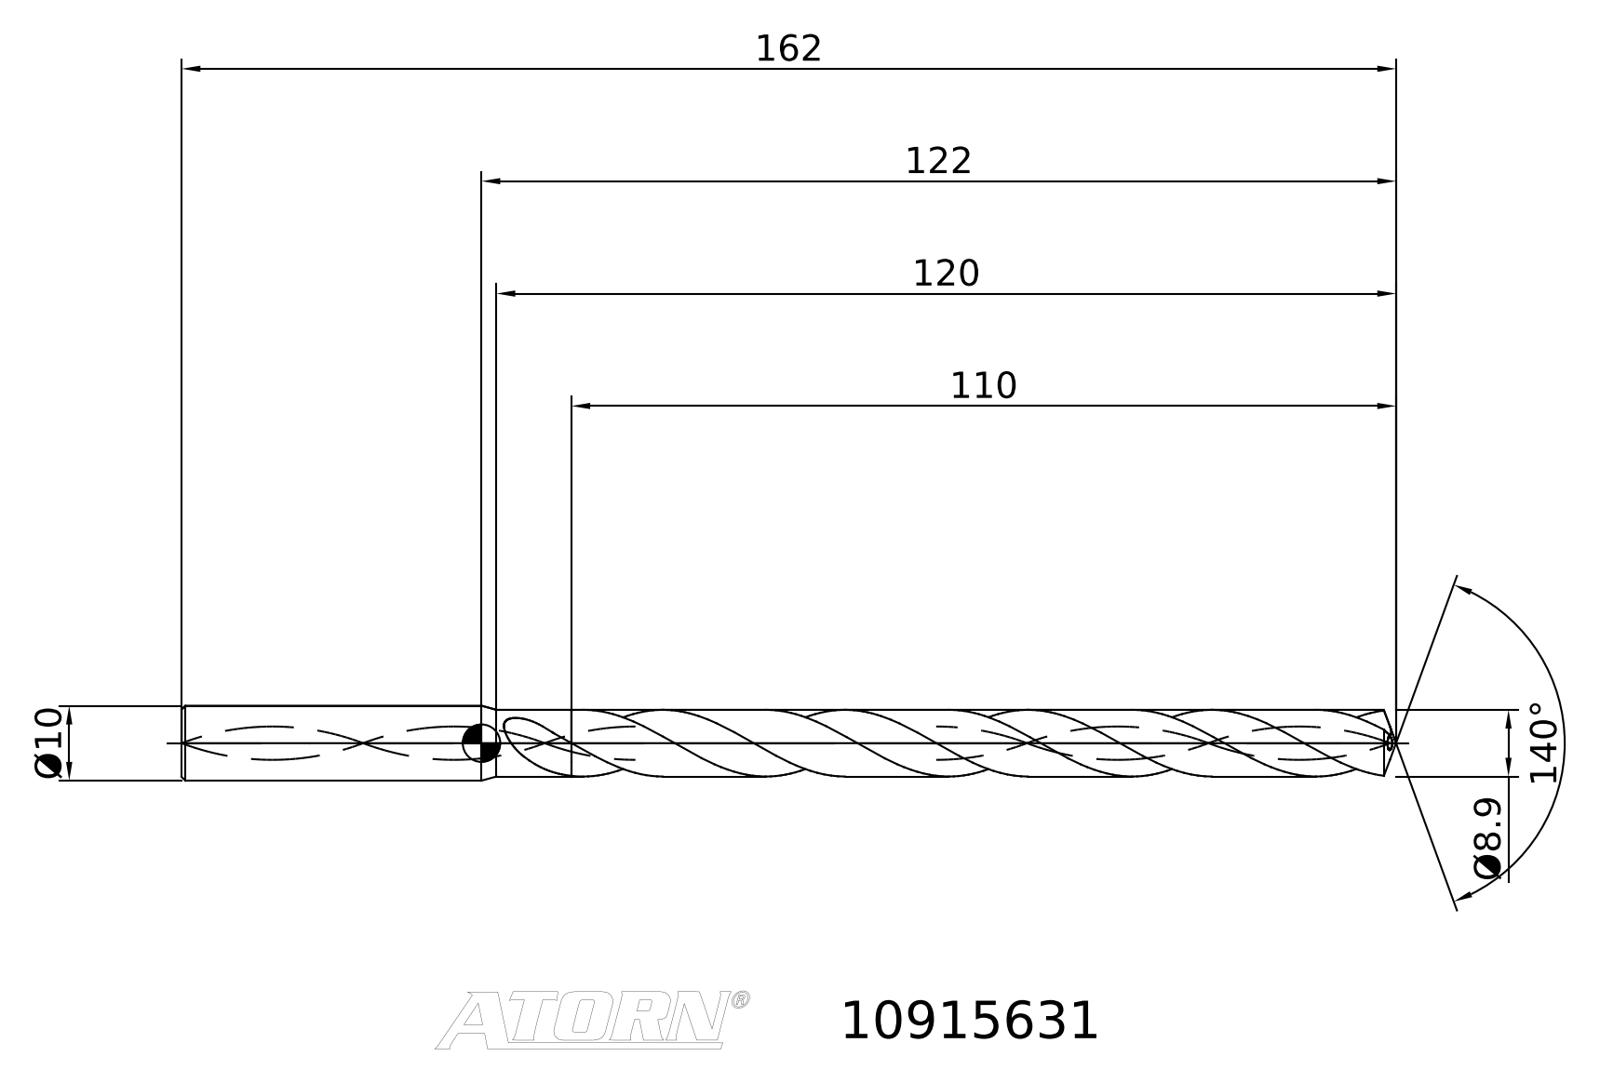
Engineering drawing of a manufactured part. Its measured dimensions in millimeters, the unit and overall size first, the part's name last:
Units: millimetres
Overall size (bounding box): 162 × 10 × 10
Main face-to-face distances: 52, 108.79, 160.79
Volume: 8 166 mm³ · Surface area: 5 166 mm²
Bodies: 2 solids, 33 faces (5 planar, 0 cylindrical, 28 other)
STEP written by: TDM (AUTOMOTIVE_DESIGN)
